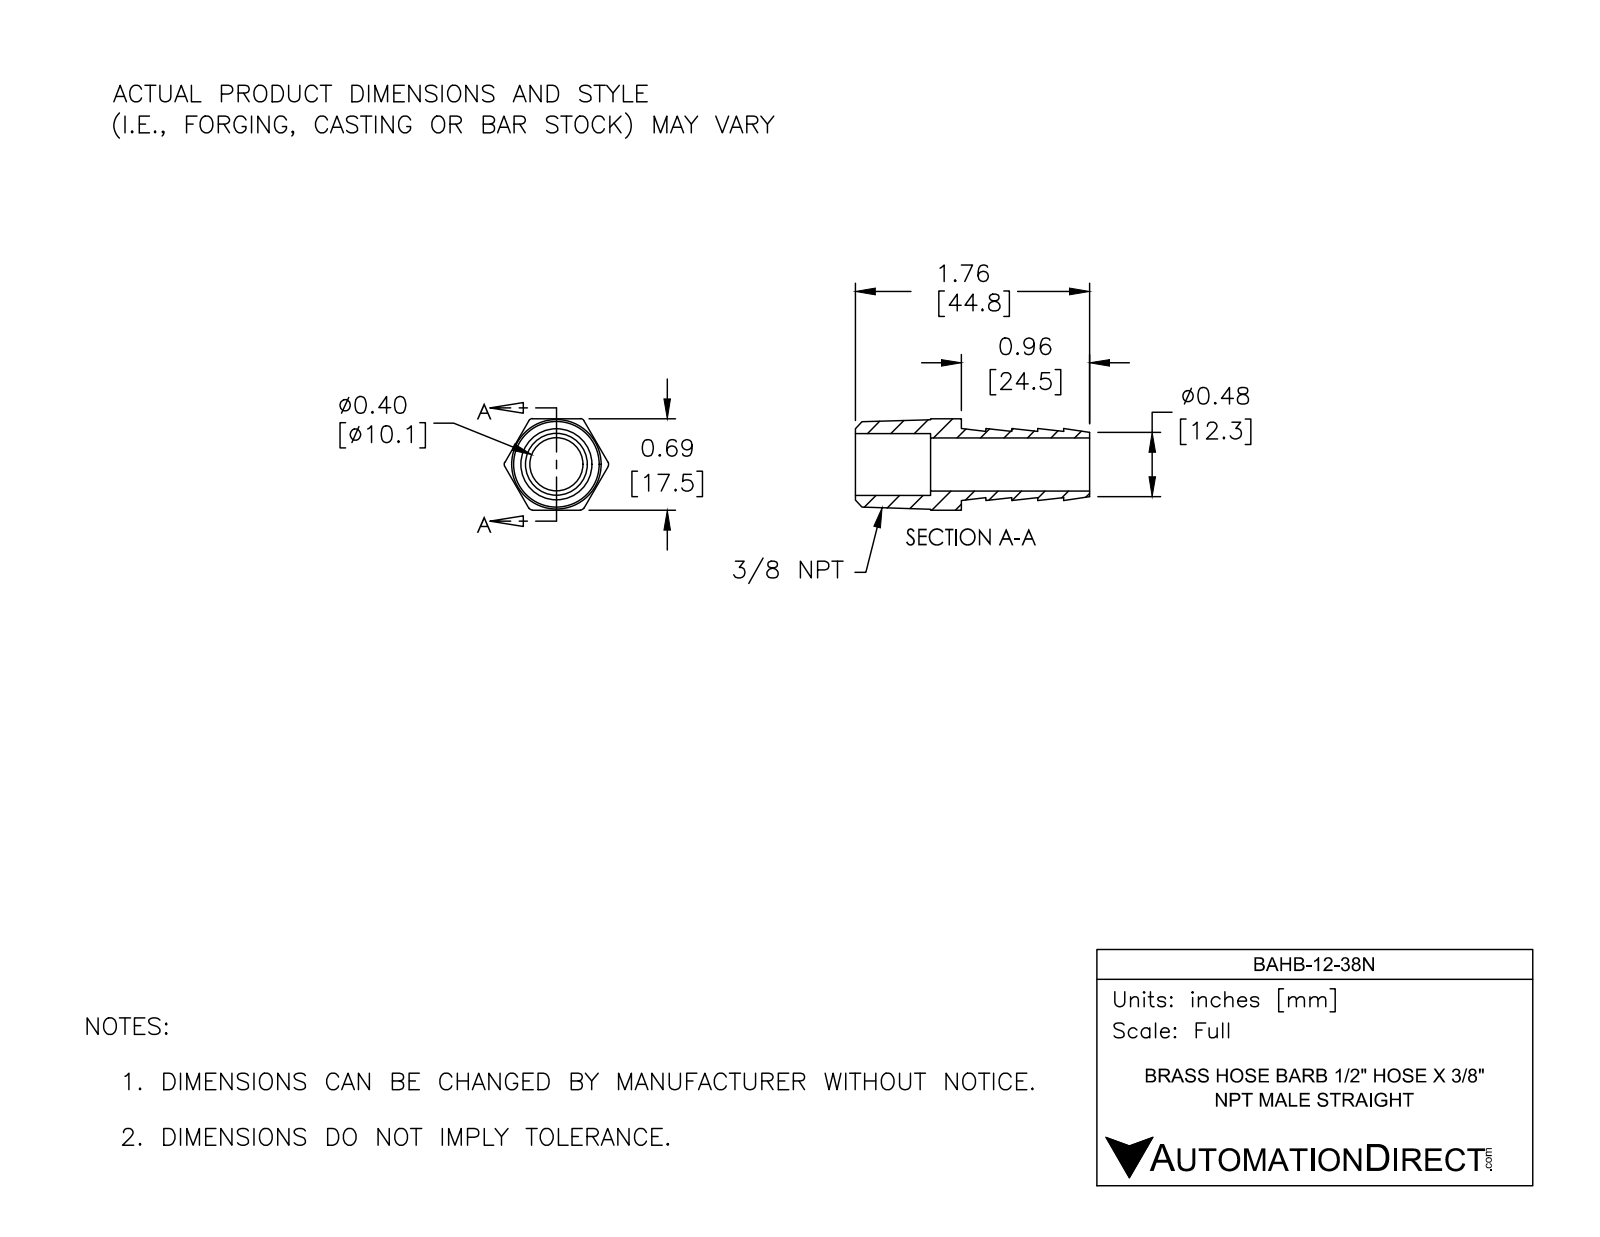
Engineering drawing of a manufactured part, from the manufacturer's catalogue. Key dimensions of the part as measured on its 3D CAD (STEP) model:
Part name (STEP PRODUCT): BAHB-12-38N
STEP written by: SolidWorks 2017 (AUTOMOTIVE_DESIGN)
Units: inches
Bodies: 1 solid, 39 faces (15 planar, 10 cylindrical, 14 other)
Overall size (bounding box): 1.762 × 0.785 × 0.687
Volume: 0.243 in³ · Surface area: 6.212 in²
Round holes (diameter × count): ⌀0.399 ×1, ⌀0.465 ×1
Partial cylindrical surfaces — rounded edges, fillets, slot ends (radius × count): R0.03 ×6
Main face-to-face distances: 0.687, 0.195, 0.232, 0.585, 0.39, 0.964, 1.196, 1.762, 0.798, 0.566
